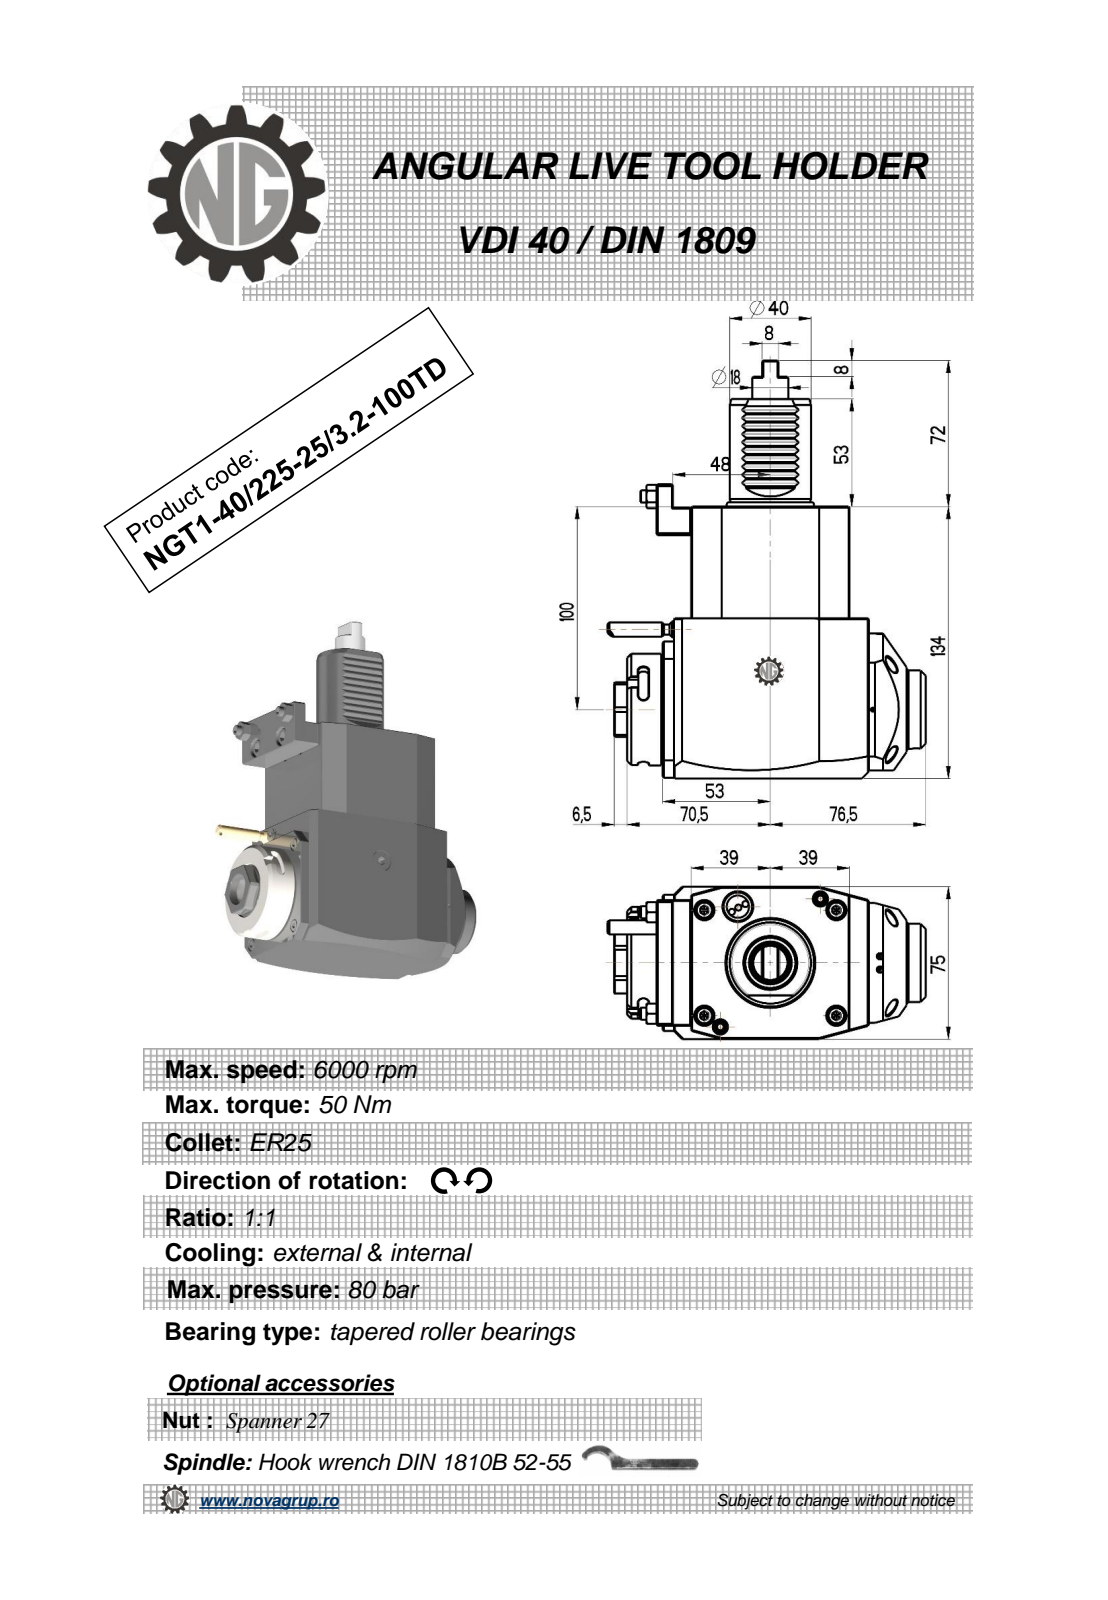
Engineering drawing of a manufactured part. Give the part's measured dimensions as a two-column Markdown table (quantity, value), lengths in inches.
| quantity | value |
| --- | --- |
| part name | NGT1_40_225_25_3_2_100TD |
| STEP written by | PRO/ENGINEER BY PARAMETRIC TECHNOLOGY CORPORATION, 2010280 (CONFIG_CONTROL_DESIGN) |
| units | inches |
| bodies | 1 solid, 378 faces (188 planar, 86 cylindrical, 104 other) |
| overall size | 8.11 × 6.174 × 2.953 |
| volume | 66.21 in³ |
| surface area | 121.7 in² |
| round holes (diameter × count) | 0.079 × 2, 0.102 × 2, 0.098 × 1, 0.118 × 1, 0.709 × 1 |
| round bosses / shafts (diameter × count) | 1.575 × 2, 0.236 × 2, 2.165 × 1, 1.89 × 1, 1.516 × 1, 0.701 × 1, 0.315 × 1, 0.276 × 1 |
| partial cylindrical surfaces (radius × count) | 0.012 × 10, 0.012 × 10, 0.008 × 6, 0.098 × 6, 0.031 × 2, 7.087 × 2, 0.02 × 1, 0.591 × 1 |
| main face-to-face distances | 2.953, 5.276, 0.551, 3.071, 3.622, 0.02, 0.669, 0.689, 0.571, 4.311 |
| hole center spacings | 0.561, 1.122, 1.56, 1.701, 1.995 |
